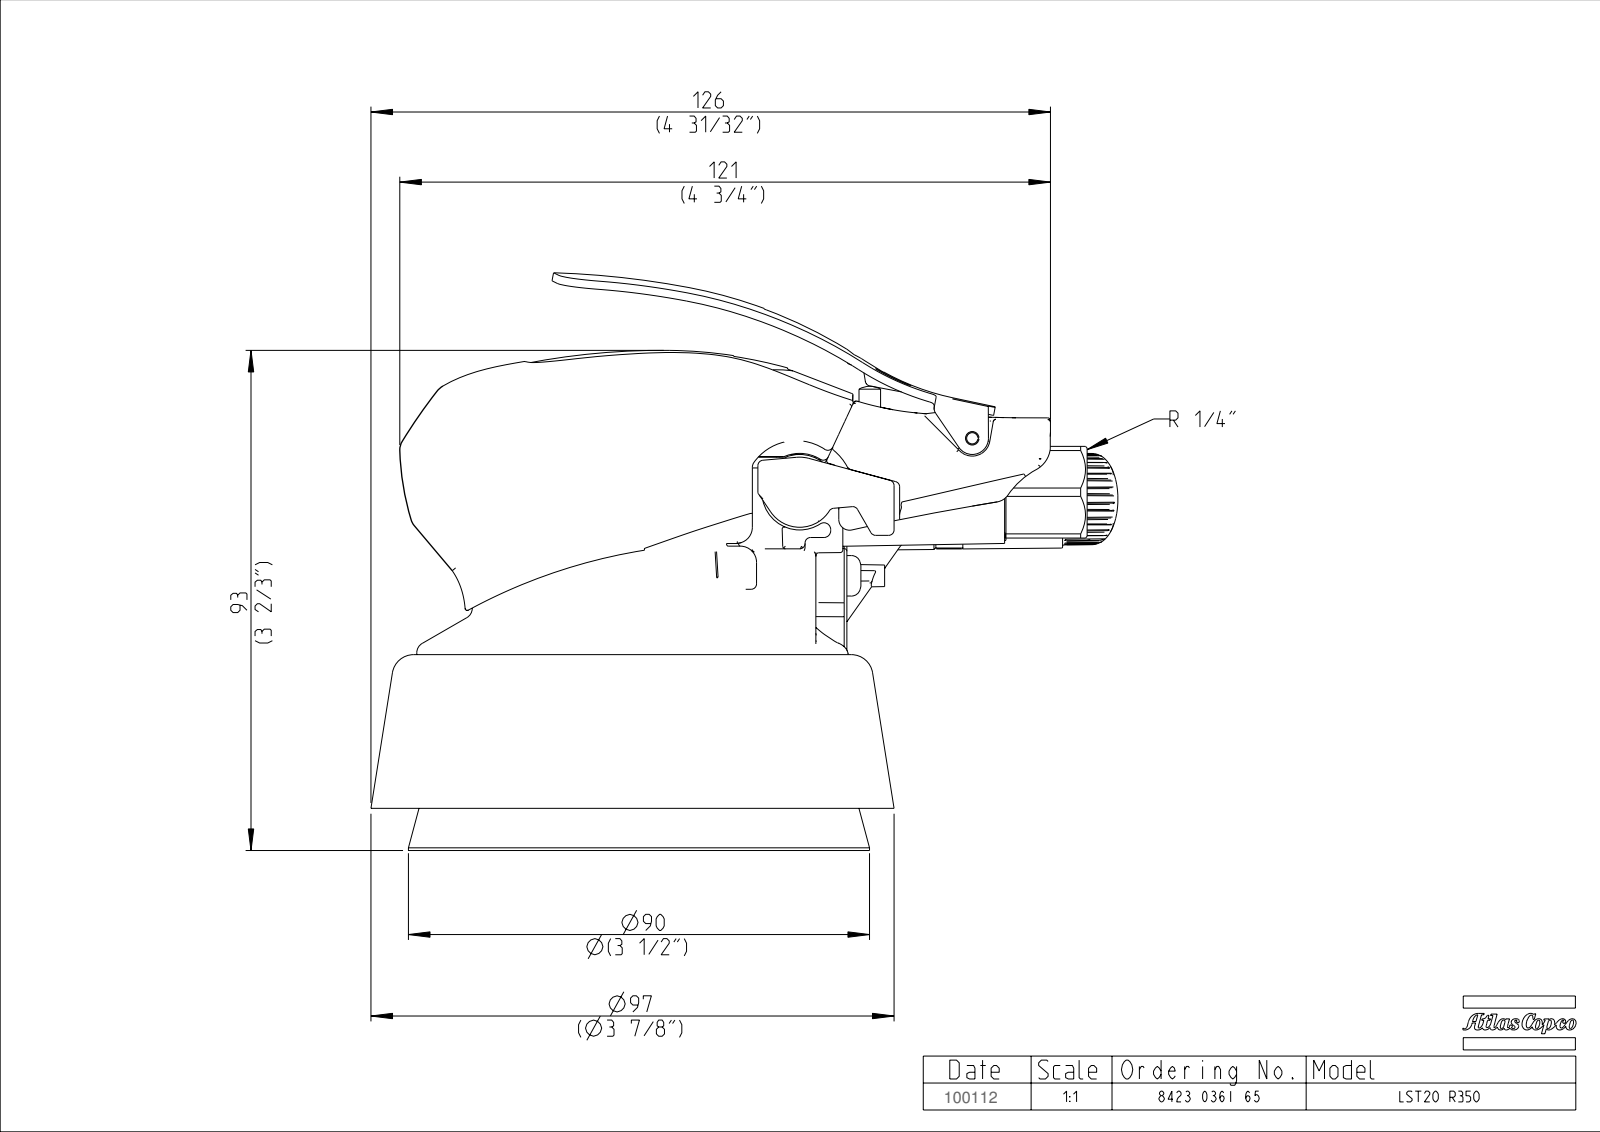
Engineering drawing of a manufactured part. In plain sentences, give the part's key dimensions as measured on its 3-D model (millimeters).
The part is named "TMP1006_SW". Its 3-D file was written by "PRO/ENGINEER BY PARAMETRIC TECHNOLOGY CORPORATION, 2008310 (CONFIG_CONTROL_DESIGN)". It is 0 solids with 925 faces: 145 planar, 232 cylindrical and 548 other. Overall it measures 138.5 by 107.13 by 97 millimeters. Round bosses or shafts: 1 of diameter 85.5, 1 of diameter 4, 1 of diameter 2.5. Partial cylindrical surfaces (rounded edges, fillets, slot ends): 39 of radius 0.5, 35 of radius 1, 25 of radius 0.2, 12 of radius 0.68, 11 of radius 0.15, 11 of radius 0.3, 6 of radius 0.25, 6 of radius 1.5. The main face-to-face distances are 7.82, 28.5, 36.32, 40, 29.25, 17, 10.75, 5.75, 3.5, 35.
